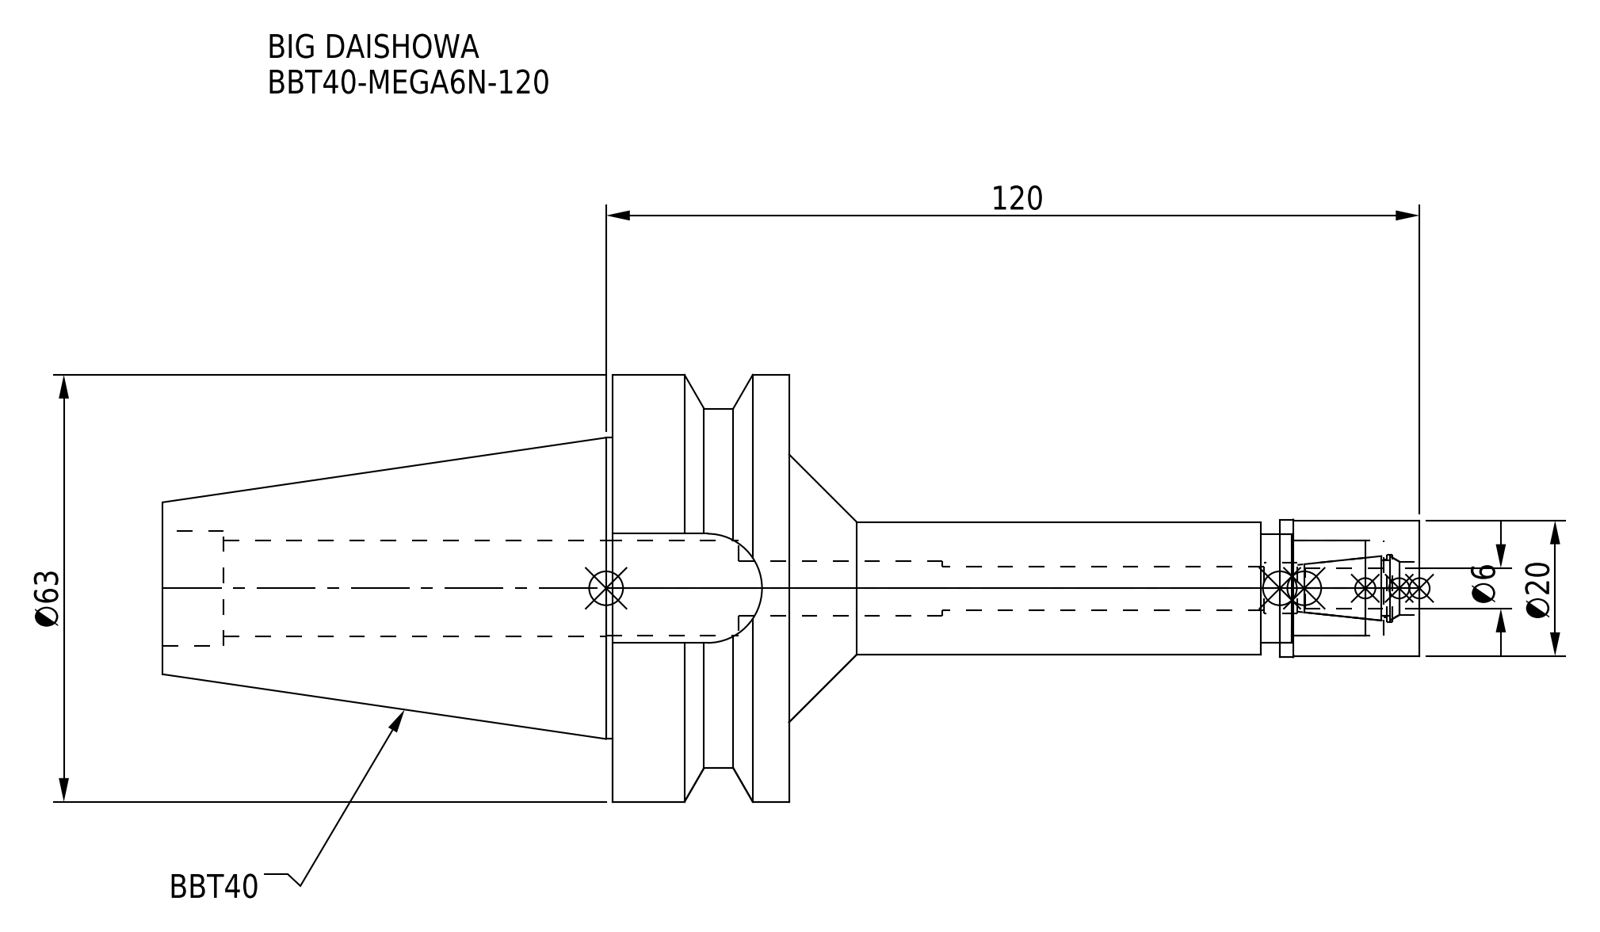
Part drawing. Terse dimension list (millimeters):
name: MGN6_1.stp; BBT40-MEGA6N-120-060.stp; BBT40-MEGA6N-120-060-FreeParts; DXF_TEMP_ASSY_ASM_4_ASM.stp (+3 more)
written by: SolidWorks 2019 (CONFIG_CONTROL_DESIGN)
unit: mm
bodies: 2 solids, 80 faces (24 planar, 42 cylindrical, 14 other)
size: 185.4 × 63 × 63
volume: 149 074 mm³; area: 32 107 mm²
holes: 1× ⌀6.4, 1× ⌀7.5, 1× ⌀7.9, 1× ⌀8, 1× ⌀8.5, 1× ⌀10, 1× ⌀14, 1× ⌀14.2, 1× ⌀16, 1× ⌀17
bosses: 1× ⌀63, 1× ⌀53, 1× ⌀44.45, 1× ⌀20.3, 1× ⌀20, 1× ⌀19.5
rounds: 1× R8.05
face distances: 26, 92.4, 45, 66.4, 93, 119, 185.4, 16.1, 85, 18.6
